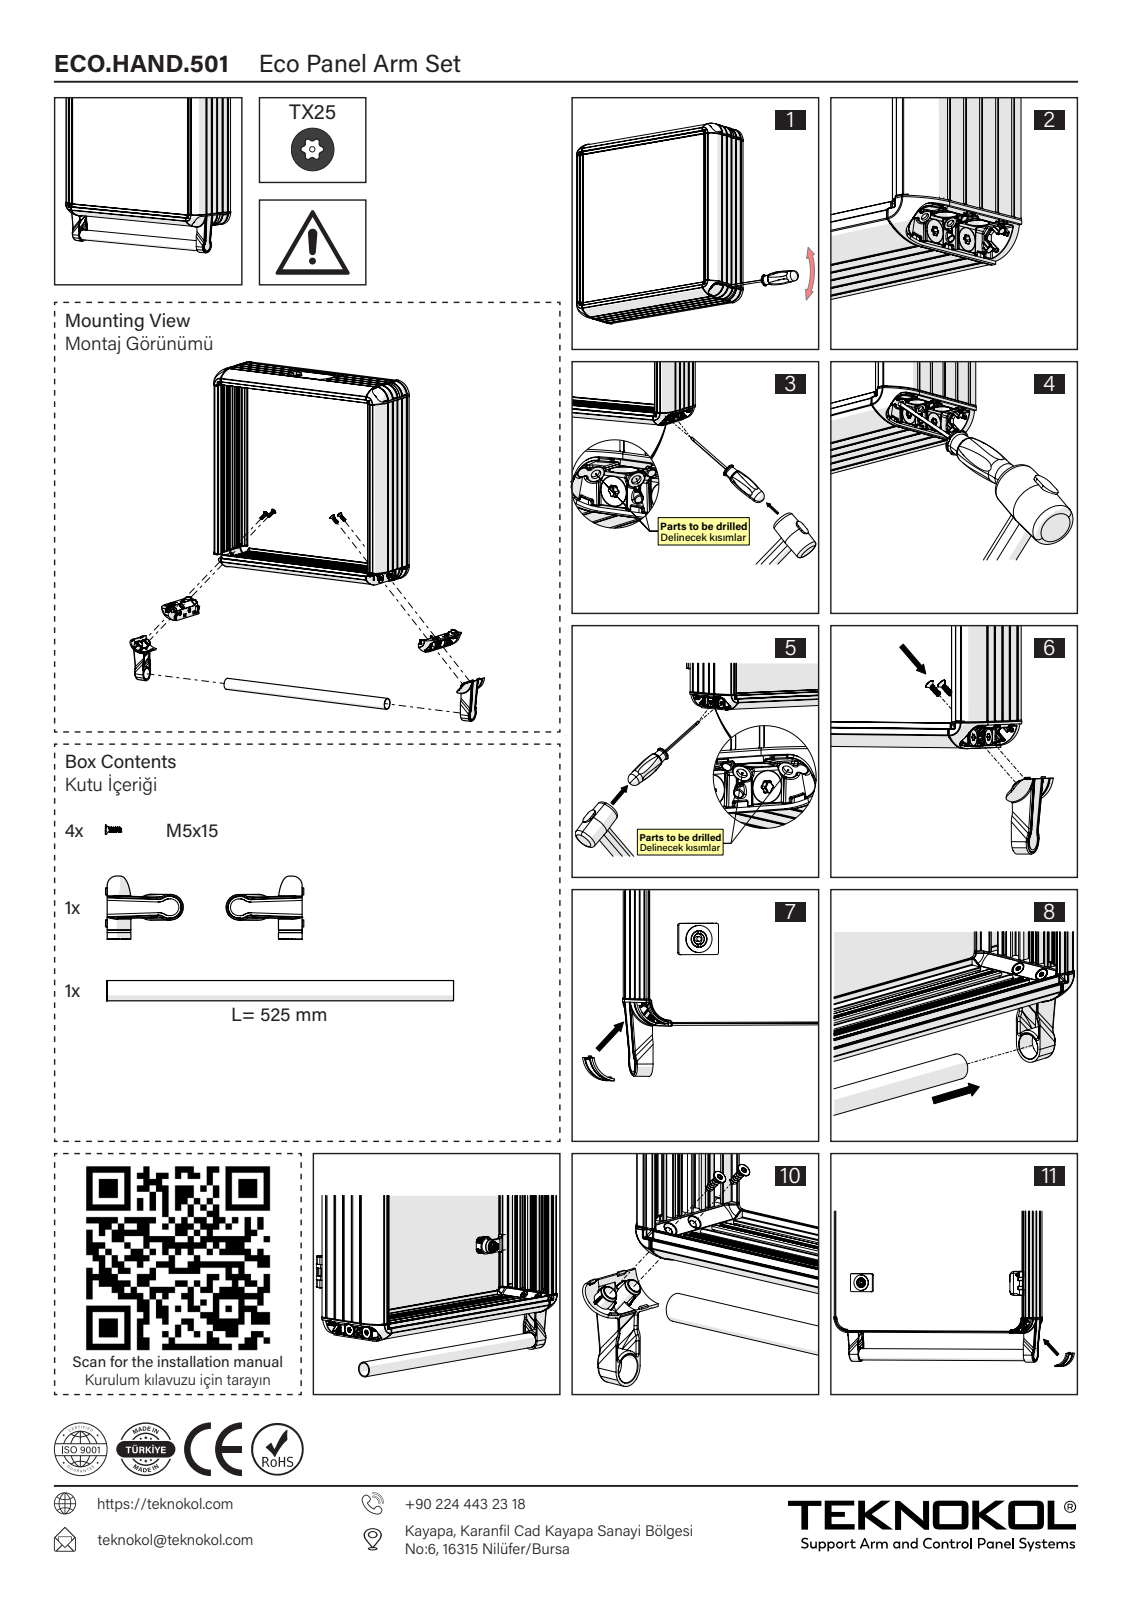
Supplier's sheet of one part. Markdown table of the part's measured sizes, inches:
| quantity | value |
| --- | --- |
| part name | ECO.HAND.501 |
| STEP written by | SolidWorks 2023 (AUTOMOTIVE_DESIGN) |
| units | inches |
| bodies | 11 solids, 869 faces (196 planar, 286 cylindrical, 387 other) |
| overall size | 20.669 × 3.187 × 0.934 |
| volume | 3.603 in³ |
| surface area | 137 in² |
| round holes (diameter × count) | 0.197 × 4, 0.354 × 4, 0.748 × 2, 0.669 × 1 |
| round bosses / shafts (diameter × count) | 0.354 × 4, 0.11 × 4, 0.748 × 1 |
| partial cylindrical surfaces (radius × count) | 0.012 × 68, 0.016 × 24, 0.068 × 16, 0.059 × 14, 0.039 × 12, 0.118 × 12, 0.047 × 8, 0.054 × 4 |
| main face-to-face distances | 0.098, 0.09, 0.019, 0.472, 0.453, 0.02, 0.018, 0.099, 0.059, 7.15 |
| hole center spacings | 0.945, 1.18 |
